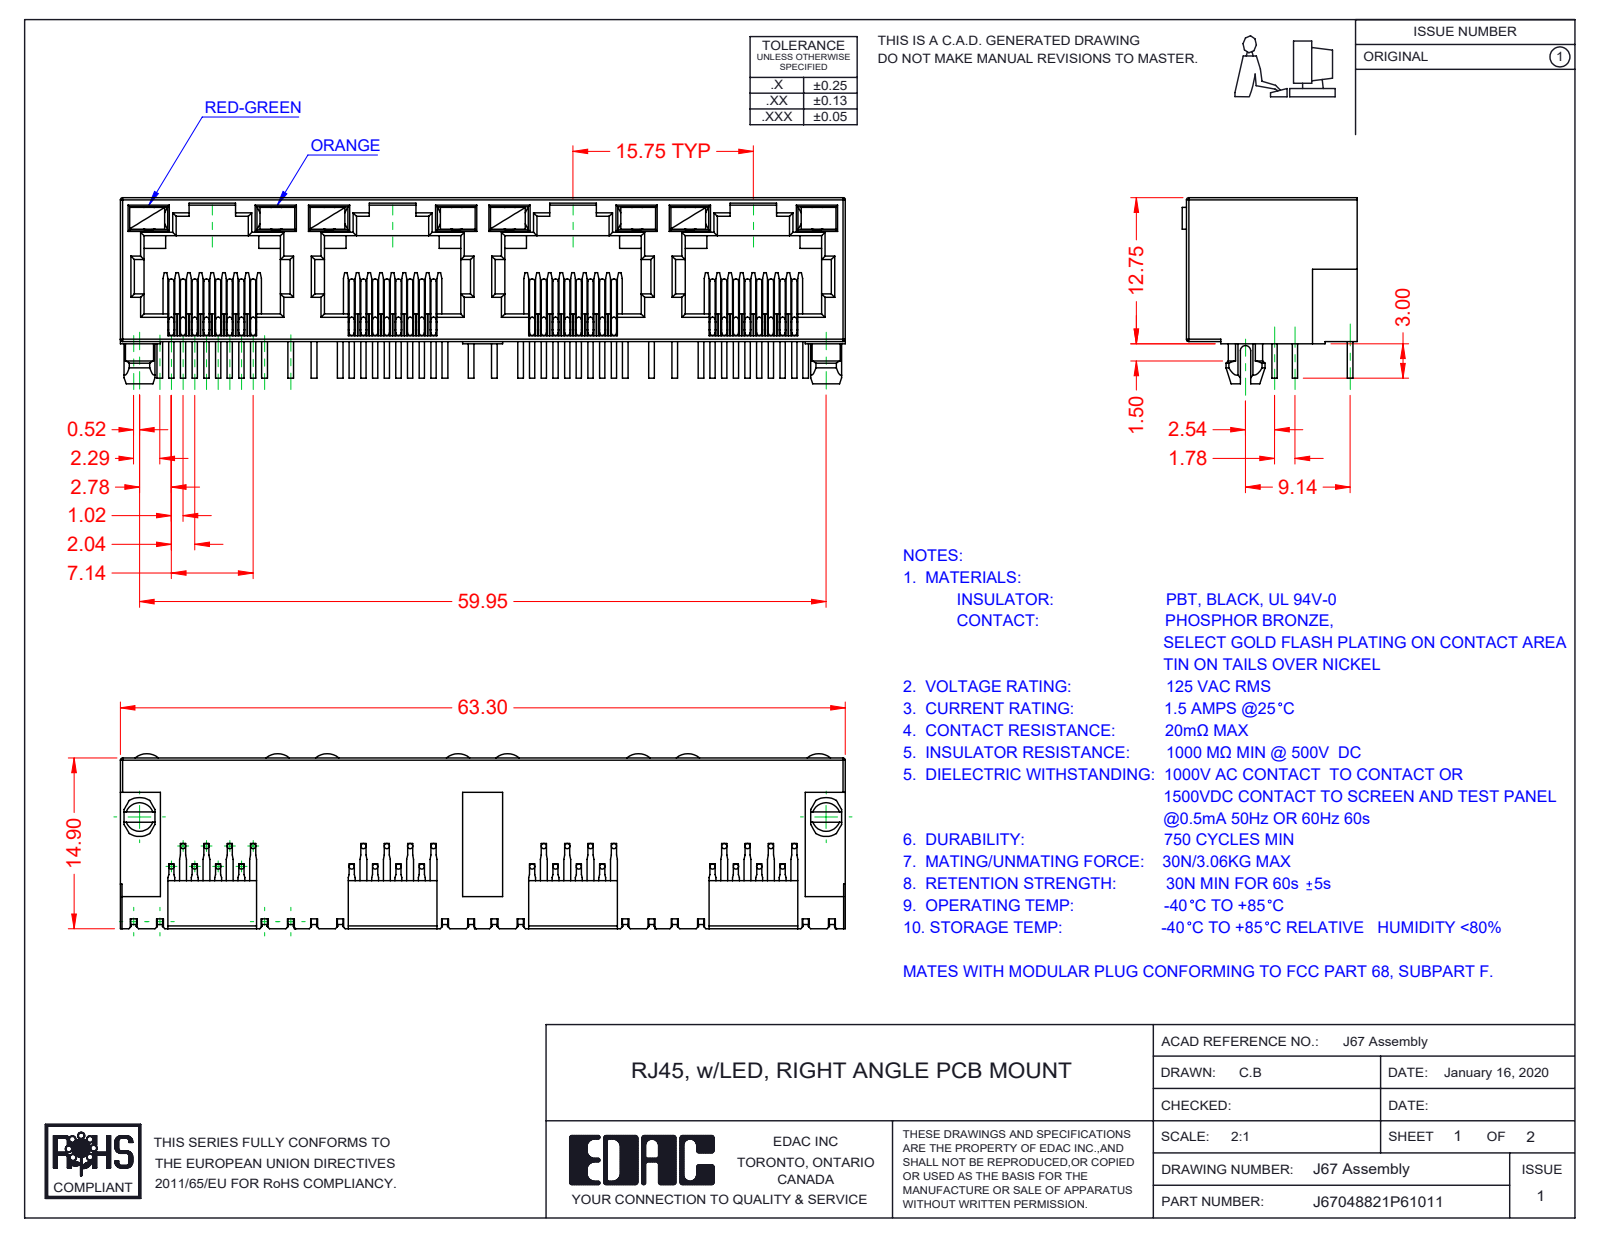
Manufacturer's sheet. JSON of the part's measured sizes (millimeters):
{"part_name": "67 Contacts; 67 LED RH_4-Orange; 67 LED LH_6-Red-Green; J67048822P64011 (+1 more)", "step_written_by": "SolidWorks 2016 (CONFIG_CONTROL_DESIGN)", "units": "millimeters", "bodies": {"solids": 41, "faces": 2473, "planar": 1781, "cylindrical": 484, "other": 208}, "overall_size": [63.3, 16.25, 15.28], "volume_mm3": 5159, "surface_area_mm2": 11573, "round_bosses_or_shafts": [[0.46, 96]], "partial_cylinders_radius": [[0.2, 66], [0.3, 29], [0.45, 9], [1.55, 8], [1.5, 2], [1.7, 2], [0.35, 1], [1, 1]], "face_to_face_distances": [0.5, 12.55, 1.89, 0.89, 10, 15.75, 1, 1.39, 11, 11.89]}
